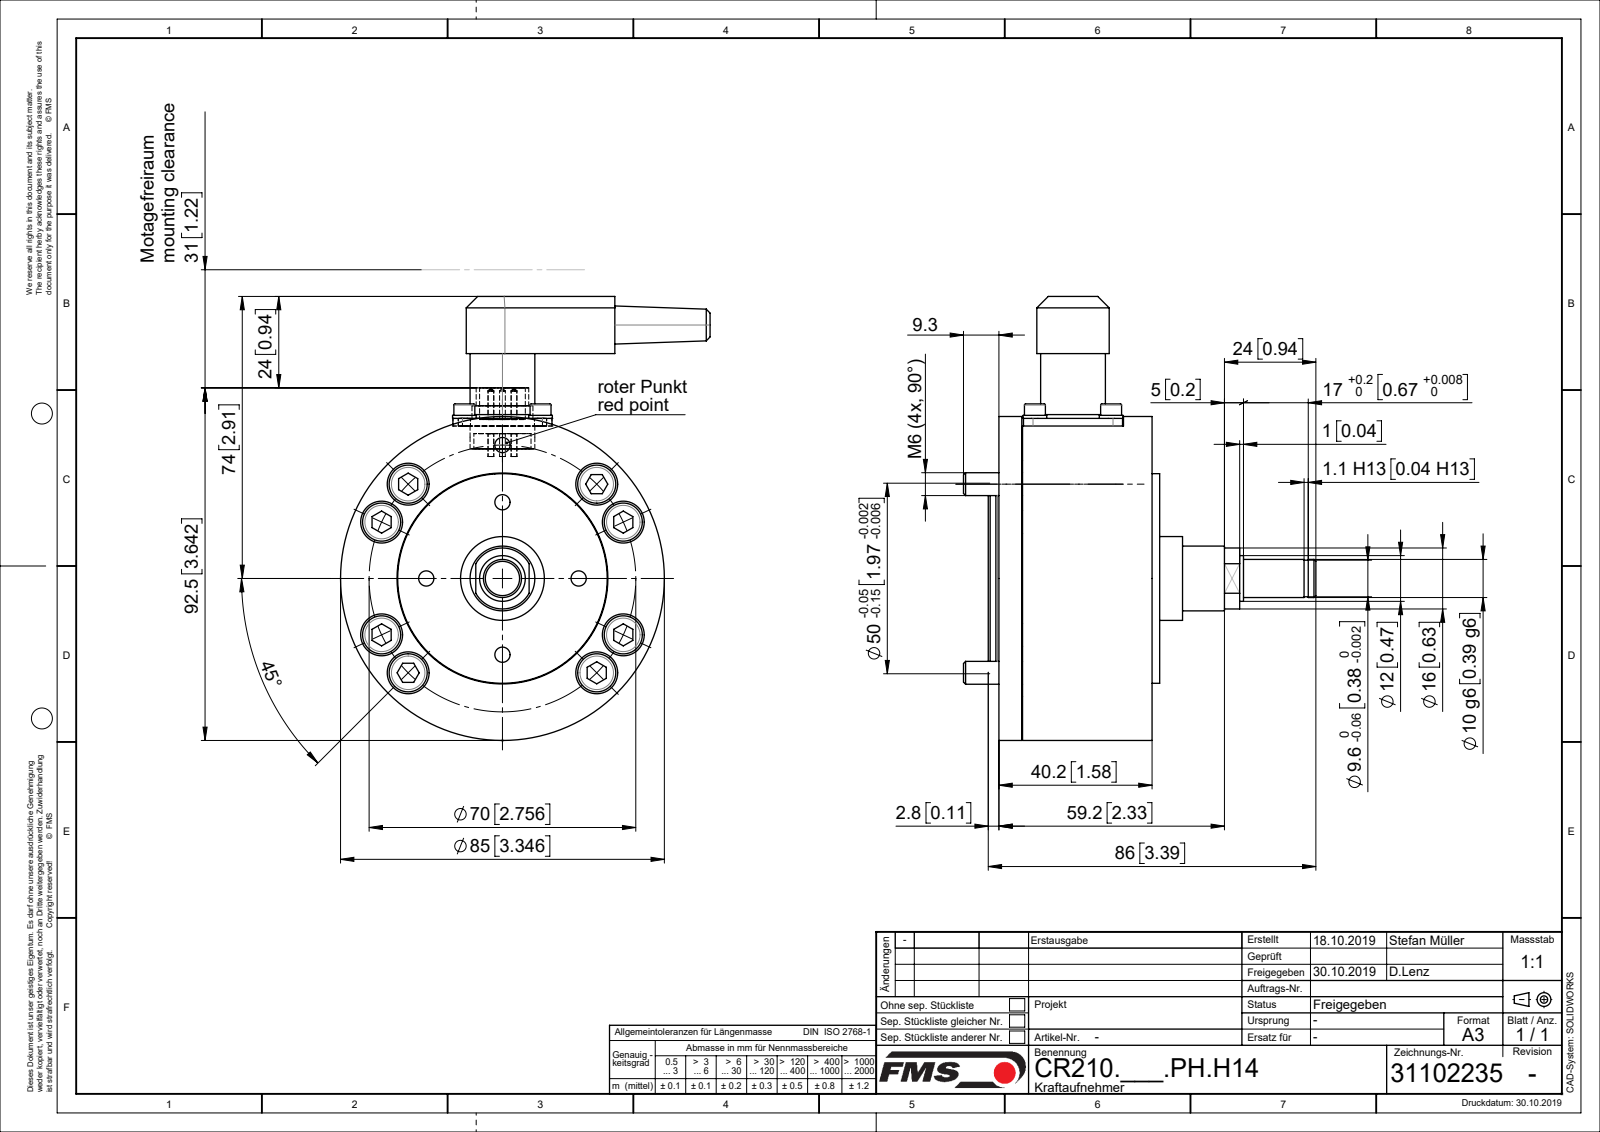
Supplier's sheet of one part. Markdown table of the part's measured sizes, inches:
| quantity | value |
| --- | --- |
| part name | 31102235_STP; C0709081; C0612056; C0709072 (+8 more) |
| STEP written by | Mechanical Desktop 2009 (CONFIG_CONTROL_DESIGN) |
| units | inches |
| bodies | 26 solids, 534 faces (187 planar, 248 cylindrical, 99 other) |
| overall size | 4.547 × 3.819 × 3.642 |
| volume | 14.24 in³ |
| surface area | 116.4 in² |
| round holes (diameter × count) | 0.256 × 8, 0.433 × 8, 0.079 × 5, 0.102 × 4, 0.126 × 4, 0.157 × 4, 0.203 × 4, 0.276 × 4, 0.281 × 1, 0.42 × 1, 0.472 × 1, 0.591 × 1 |
| round bosses / shafts (diameter × count) | 0.394 × 9, 0.236 × 8, 0.059 × 5, 0.244 × 4, 0.217 × 4, 0.197 × 4, 0.118 × 4, 0.669 × 2 |
| partial cylindrical surfaces (radius × count) | 0.098 × 4, 0.197 × 2, 0.315 × 1, 0.374 × 1 |
| main face-to-face distances | 0.236, 0.248, 0.106, 0.079, 1.587, 1.339, 1.35, 1.772, 0.118, 1.665 |
| hole center spacings | 0.787, 0.992, 1.378, 2.013, 1.113, 0.479, 0.557, 0.743 |
